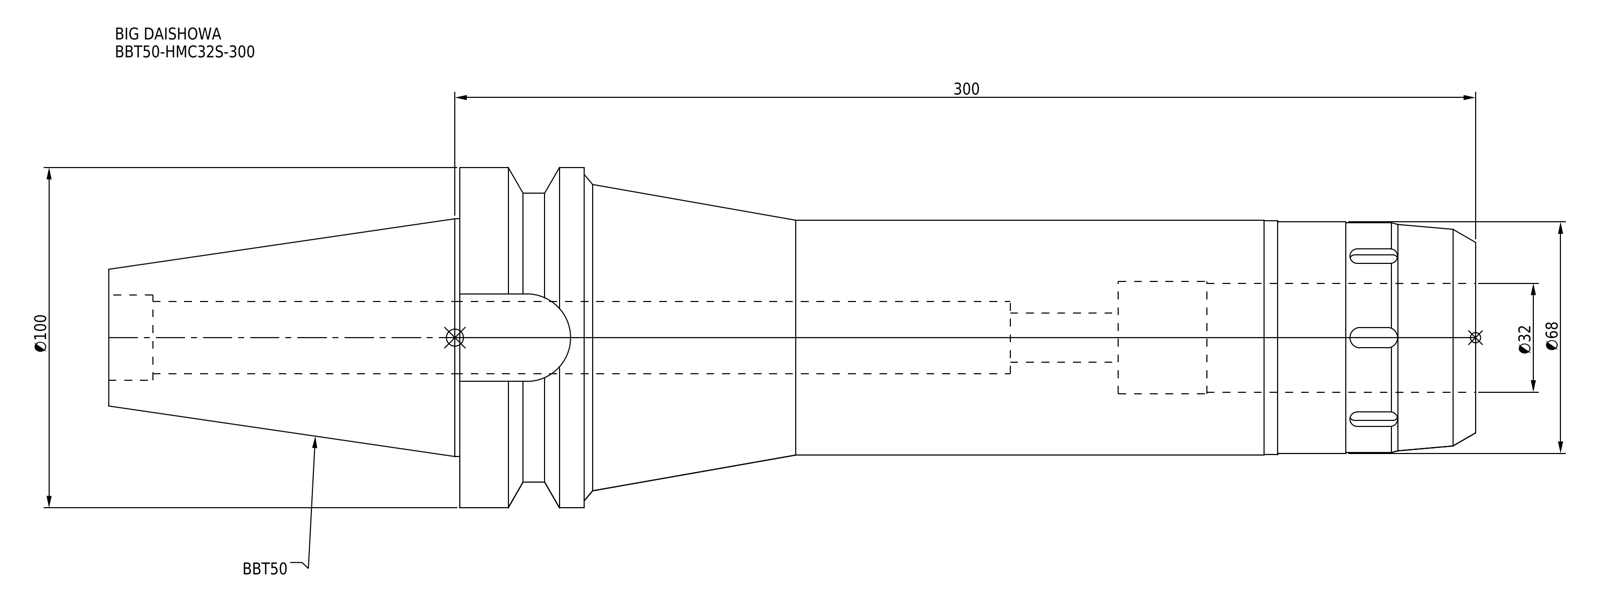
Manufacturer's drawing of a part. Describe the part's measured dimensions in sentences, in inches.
The part is named "BBT50-HMC32S-300". Its 3-D file was written by "CREO PARAMETRIC BY PTC INC, 2016380 (AUTOMOTIVE_DESIGN)". It is 1 solid with 103 faces: 39 planar, 44 cylindrical and 20 other. Overall it measures 15.819 by 3.937 by 3.937 inches. Its volume is 82.75 cubic inches and its surface area 201.8 square inches. Round holes: 1 of diameter 0.571, 1 of diameter 0.835, 1 of diameter 0.984, 1 of diameter 1.26, 1 of diameter 1.299. Round bosses or shafts: 1 of diameter 3.937, 1 of diameter 3.346, 1 of diameter 2.75, 1 of diameter 2.717, 1 of diameter 2.705, 1 of diameter 2.677, 1 of diameter 2.657. Partial cylindrical surfaces (rounded edges, fillets, slot ends): 12 of radius 0.118, 1 of radius 0.506. The main face-to-face distances are 11.752, 15.819, 4.067, 2.787, 4.134, 7.618, 11.685, 10.315, 6.181, 1.437.
